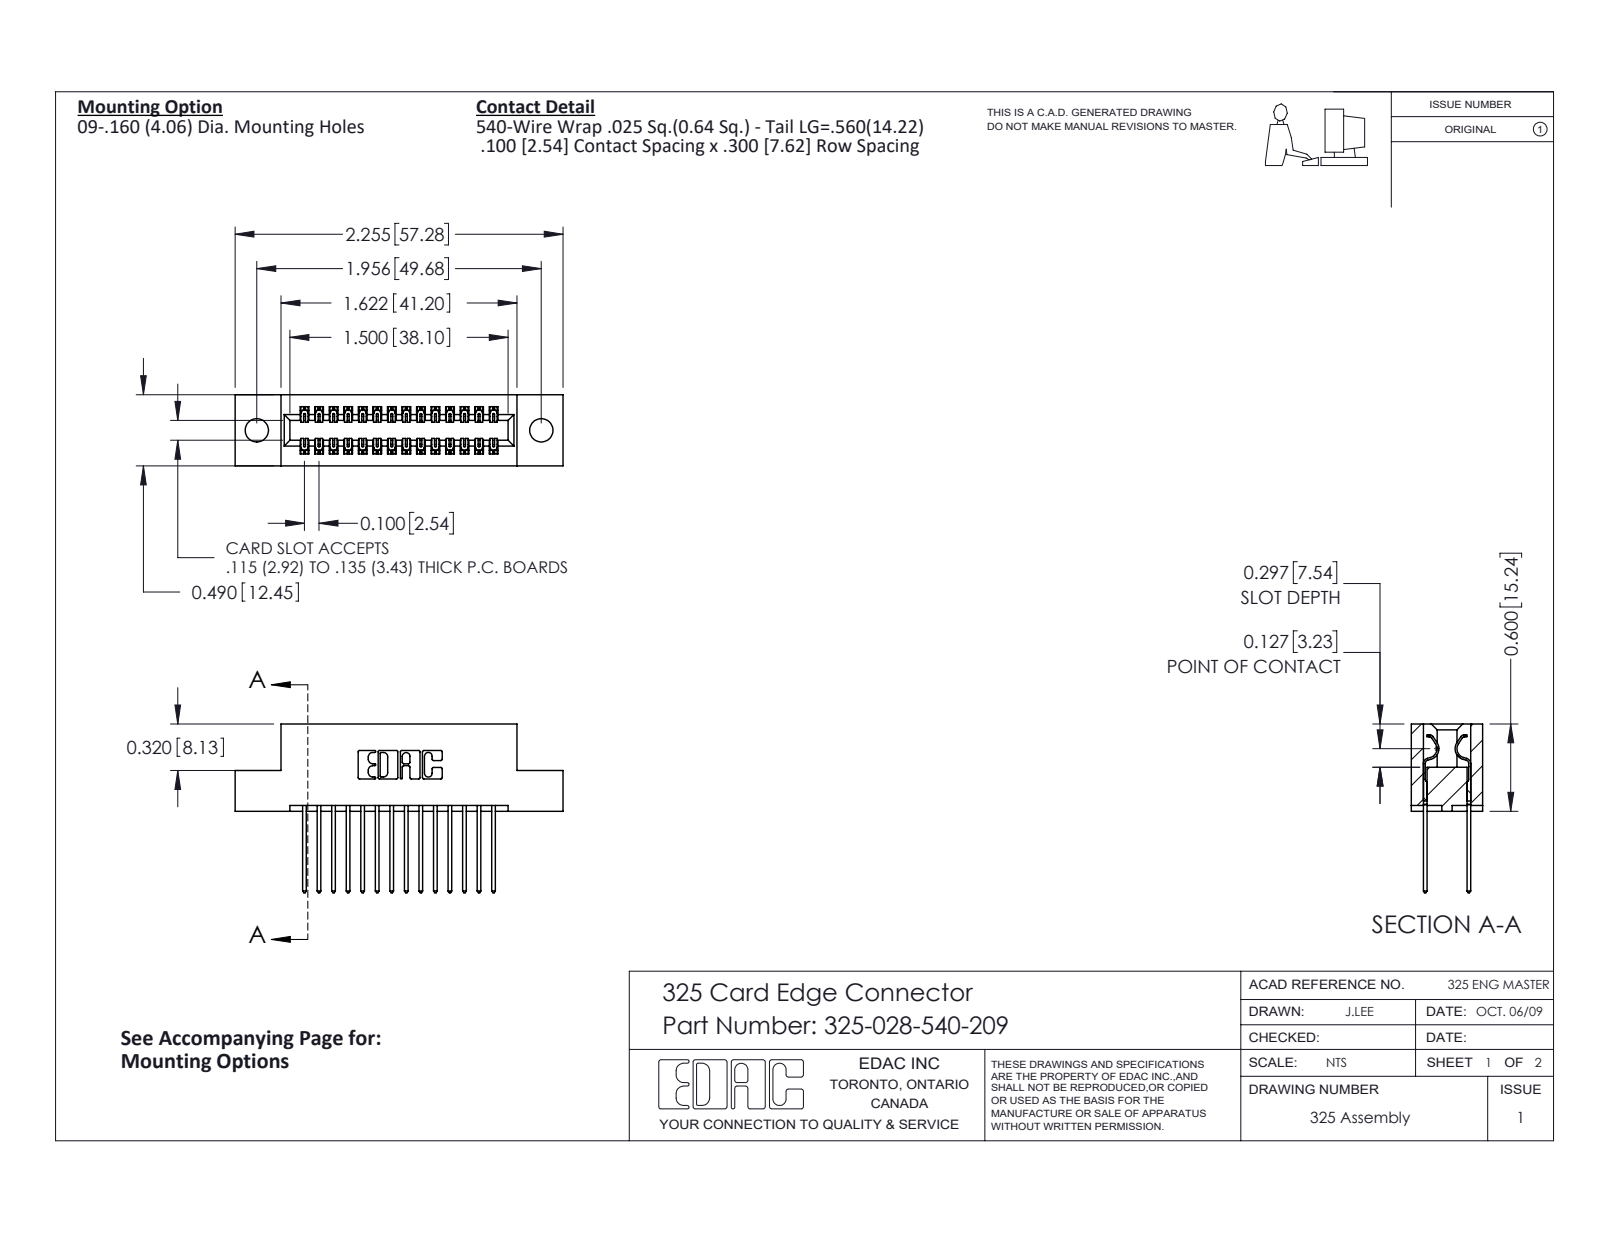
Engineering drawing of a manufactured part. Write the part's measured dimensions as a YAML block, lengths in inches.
part_name: "325-292-001_325-293-140; 325 Part_.160 TH; 325-028-540-209"
step_written_by: "SolidWorks 2016 (CONFIG_CONTROL_DESIGN)"
units: inches
bodies: {solids: 29, faces: 1570, planar: 1078, cylindrical: 492, other: 0}
overall_size: [2.255, 1.16, 0.49]
volume: 0.428
surface_area: 12.8
round_holes:
  - {diameter: 0.16, count: 2}
partial_cylinders:
  - {radius: 0.006, count: 42}
  - {radius: 0.01, count: 28}
  - {radius: 0.01, count: 22}
  - {radius: 0.007, count: 6}
  - {radius: 0.031, count: 6}
  - {radius: 0.026, count: 3}
  - {radius: 0.014, count: 2}
  - {radius: 0.022, count: 2}
face_to_face_distances: [0.083, 0.407, 0.3, 0.107, 0.383, 0.025, 0.49, 0.325, 0.04, 0.1]
hole_center_spacings: [1.956]
